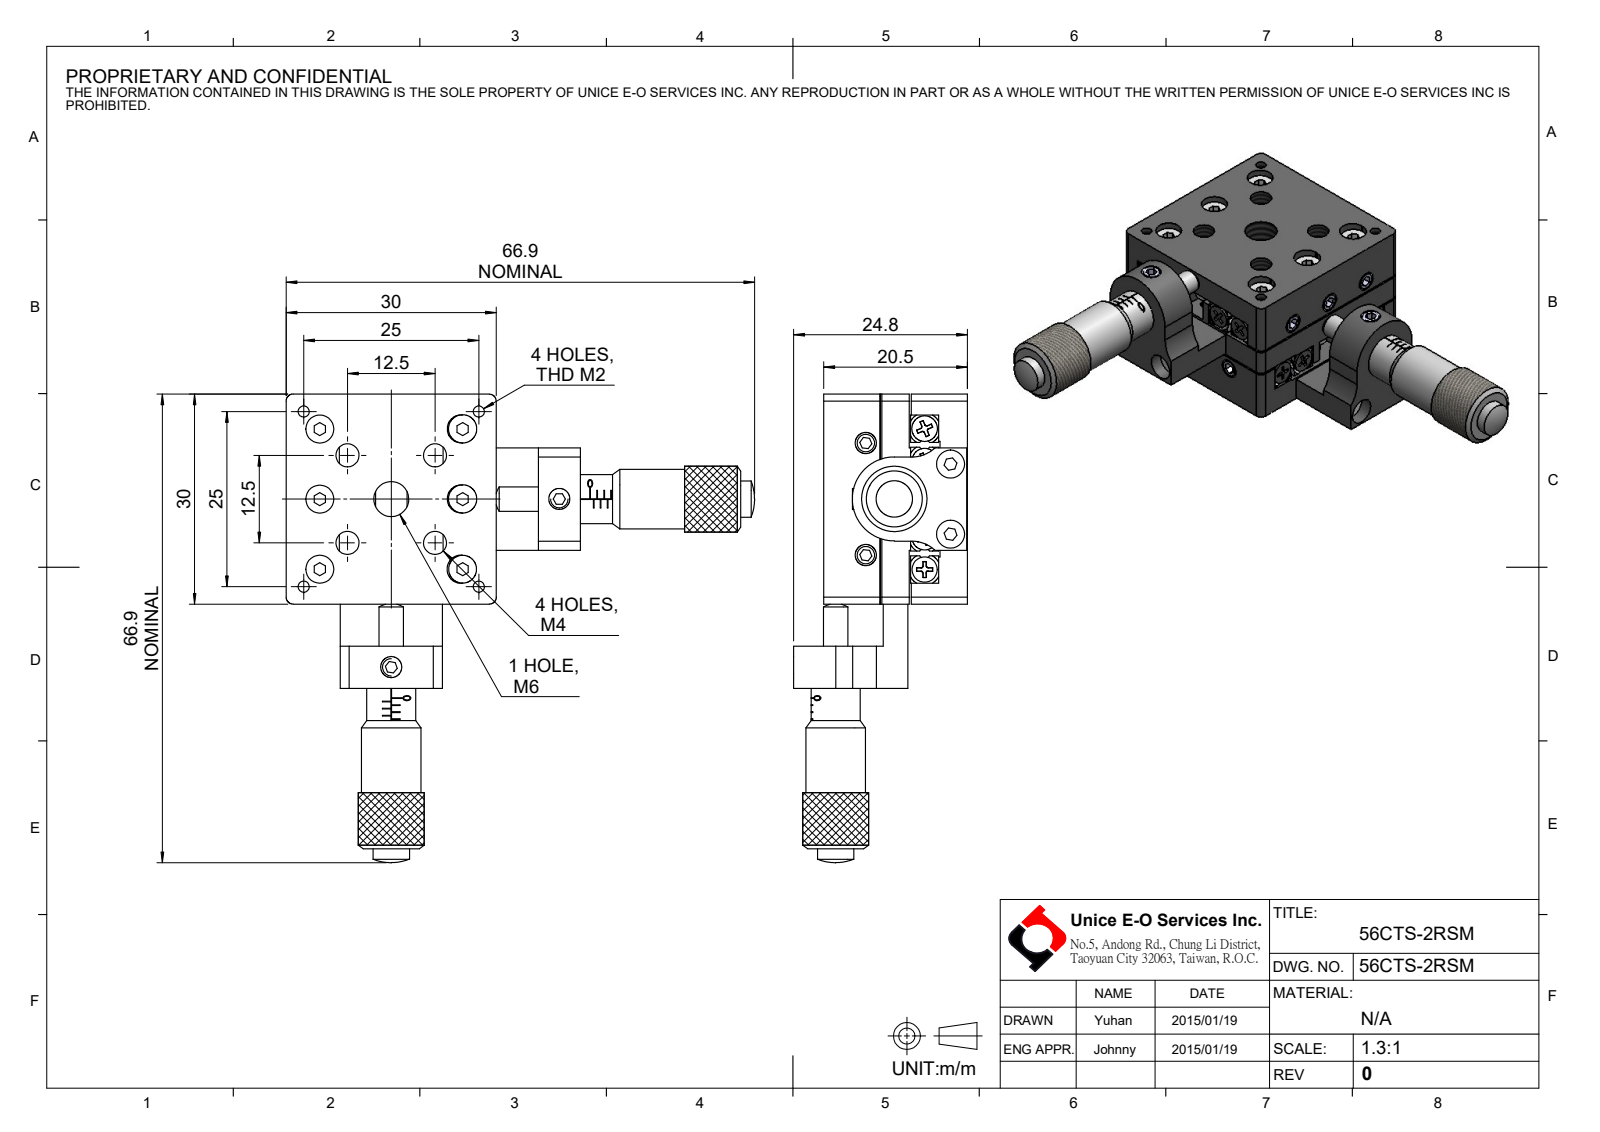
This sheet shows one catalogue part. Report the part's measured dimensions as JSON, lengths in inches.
{"part_name": "56CTS-2RSM", "step_written_by": "SolidWorks 2016 (CONFIG_CONTROL_DESIGN)", "units": "inches", "bodies": {"solids": 63, "faces": 1768, "planar": 991, "cylindrical": 505, "other": 272}, "overall_size": [2.634, 2.634, 0.976], "volume_in3": 1.25, "surface_area_in2": 37.04, "round_holes": [[0.063, 44], [0.157, 22], [0.094, 12], [0.098, 11], [0.083, 4], [0.13, 4], [0.102, 3], [0.165, 3], [0.118, 2], [0.138, 2], [0.236, 2], [0.197, 1]], "round_bosses_or_shafts": [[0.079, 20], [0.157, 10], [0.142, 8], [0.118, 8], [0.077, 8], [0.37, 2], [0.335, 2], [0.276, 2]], "partial_cylinders_radius": [[0.049, 11], [0.079, 5], [0.039, 4], [0.197, 4], [0.236, 2]], "face_to_face_distances": [0.327, 0.154, 0.319, 0.161, 0.165, 0.335, 0.157, 0.488, 0.173, 0.646], "hole_center_spacings": [0.394, 0.439, 0.61, 0.193, 0.348, 0.726, 0.778, 0.209]}
